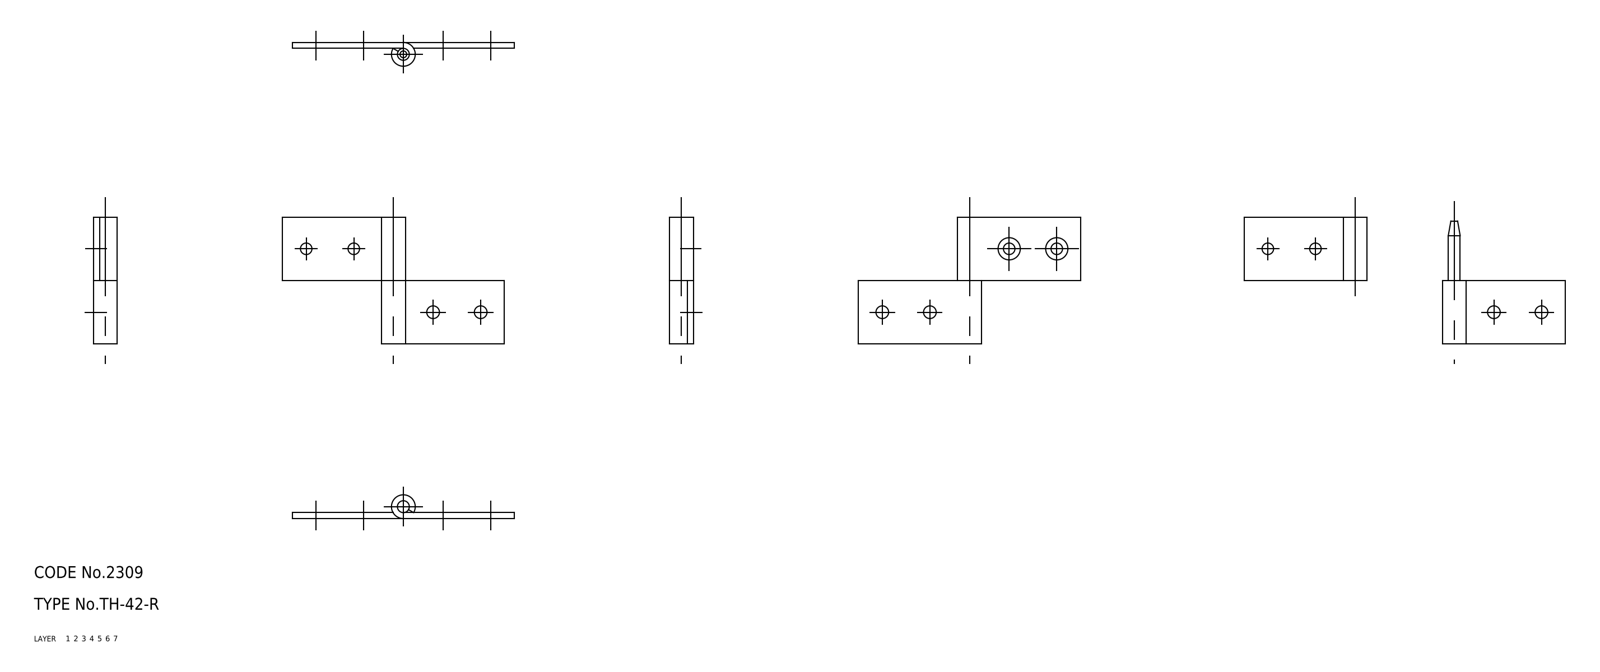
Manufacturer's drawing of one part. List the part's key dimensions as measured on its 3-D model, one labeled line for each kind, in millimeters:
Part name (STEP PRODUCT): shaft; hinge piece_B; hinge piece_A; TH_42_R_9150_36
STEP written by: CADfix (AUTOMOTIVE_DESIGN)
Units: millimetres
Bodies: 3 solids, 34 faces (0 planar, 0 cylindrical, 34 other)
Overall size (bounding box): 56 × 32 × 6
Volume: 2 052 mm³ · Surface area: 3 161 mm²
